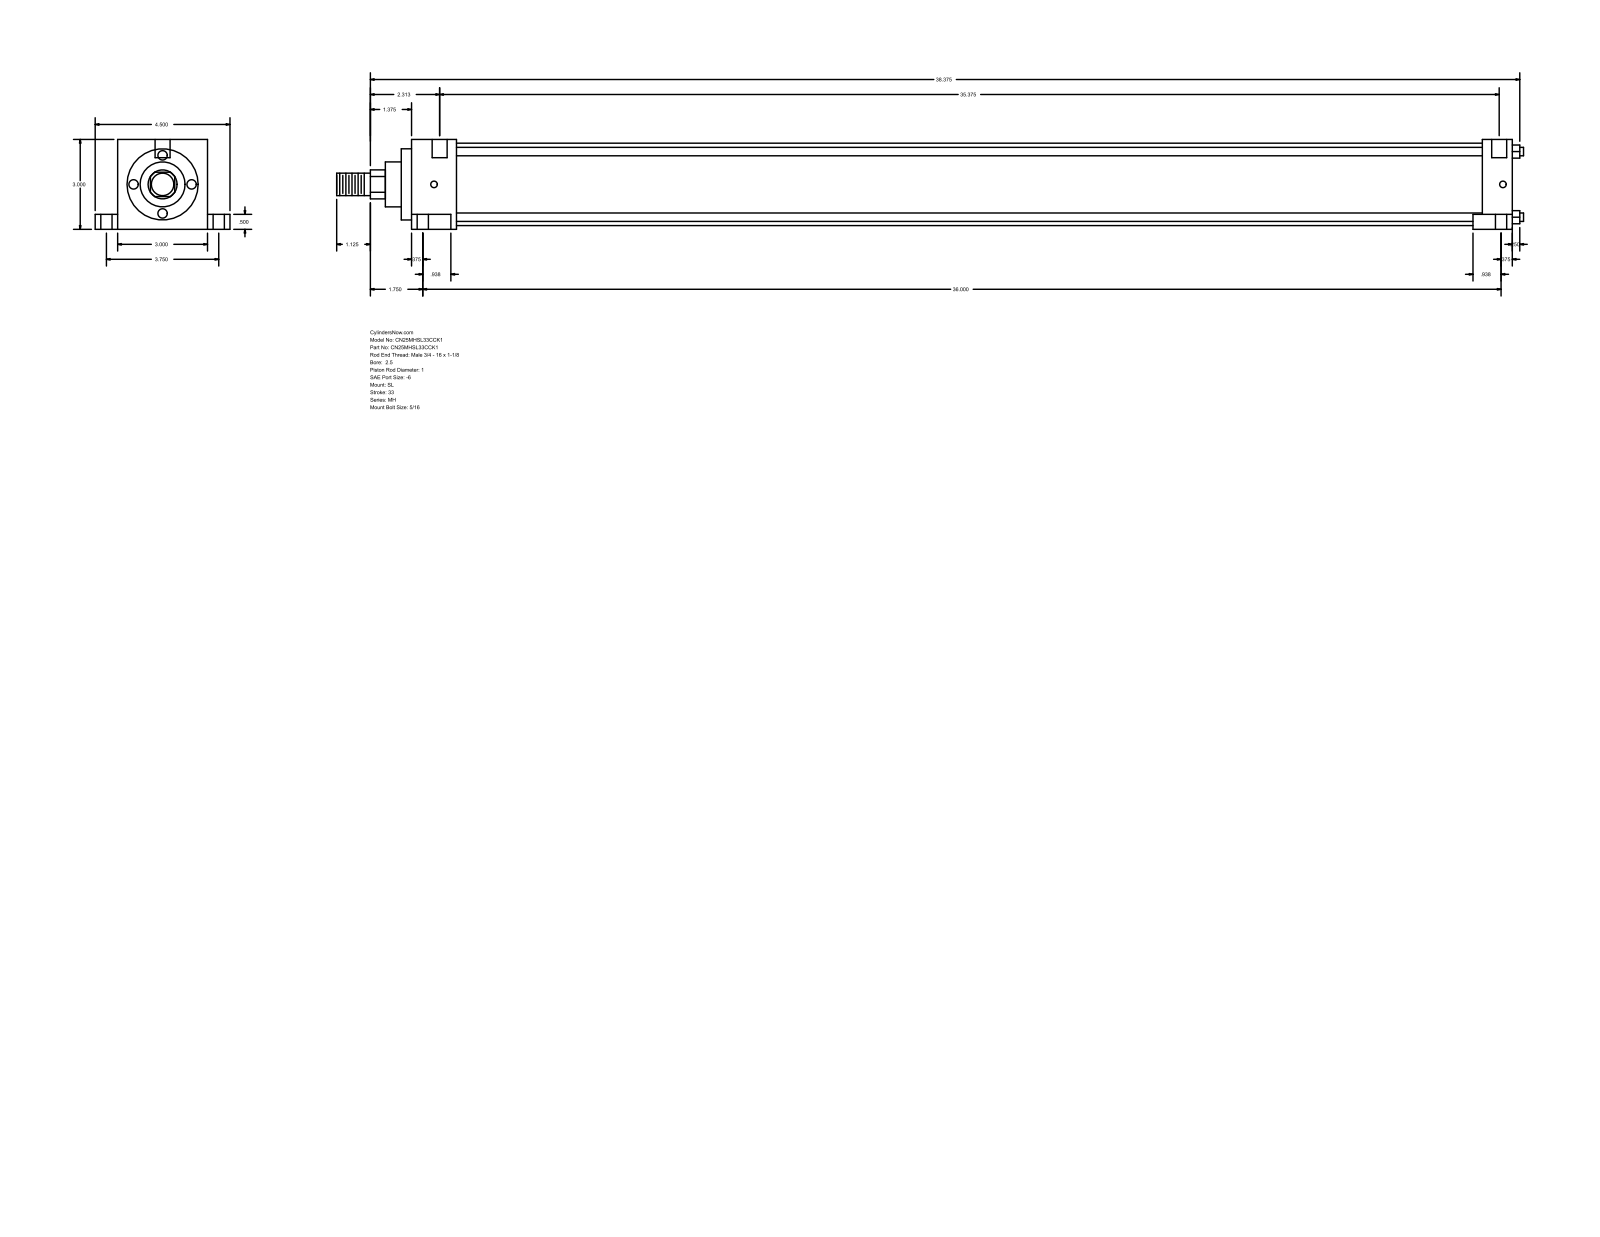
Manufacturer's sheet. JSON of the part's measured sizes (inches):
{"part_name": "MH_SL__0250_1", "step_written_by": "GSSL Pune (CONFIG_CONTROL_DESIGN)", "units": "inches", "bodies": {"solids": 0, "faces": 86, "planar": 61, "cylindrical": 25, "other": 0}, "overall_size": [39.625, 4.5, 3], "round_holes": [[0.219, 2], [0.375, 2], [0.625, 2], [0.5, 1]], "round_bosses_or_shafts": [[0.281, 4], [2.75, 1], [2.375, 1], [1.5, 1], [1, 1], [0.75, 1]], "partial_cylinders_radius": [[0.484, 1]], "face_to_face_distances": [3, 1, 36.094, 37.094, 0.5, 2.5, 0.75, 3.75, 0.531, 36.625], "hole_center_spacings": [1.876, 0.125, 3.75]}
